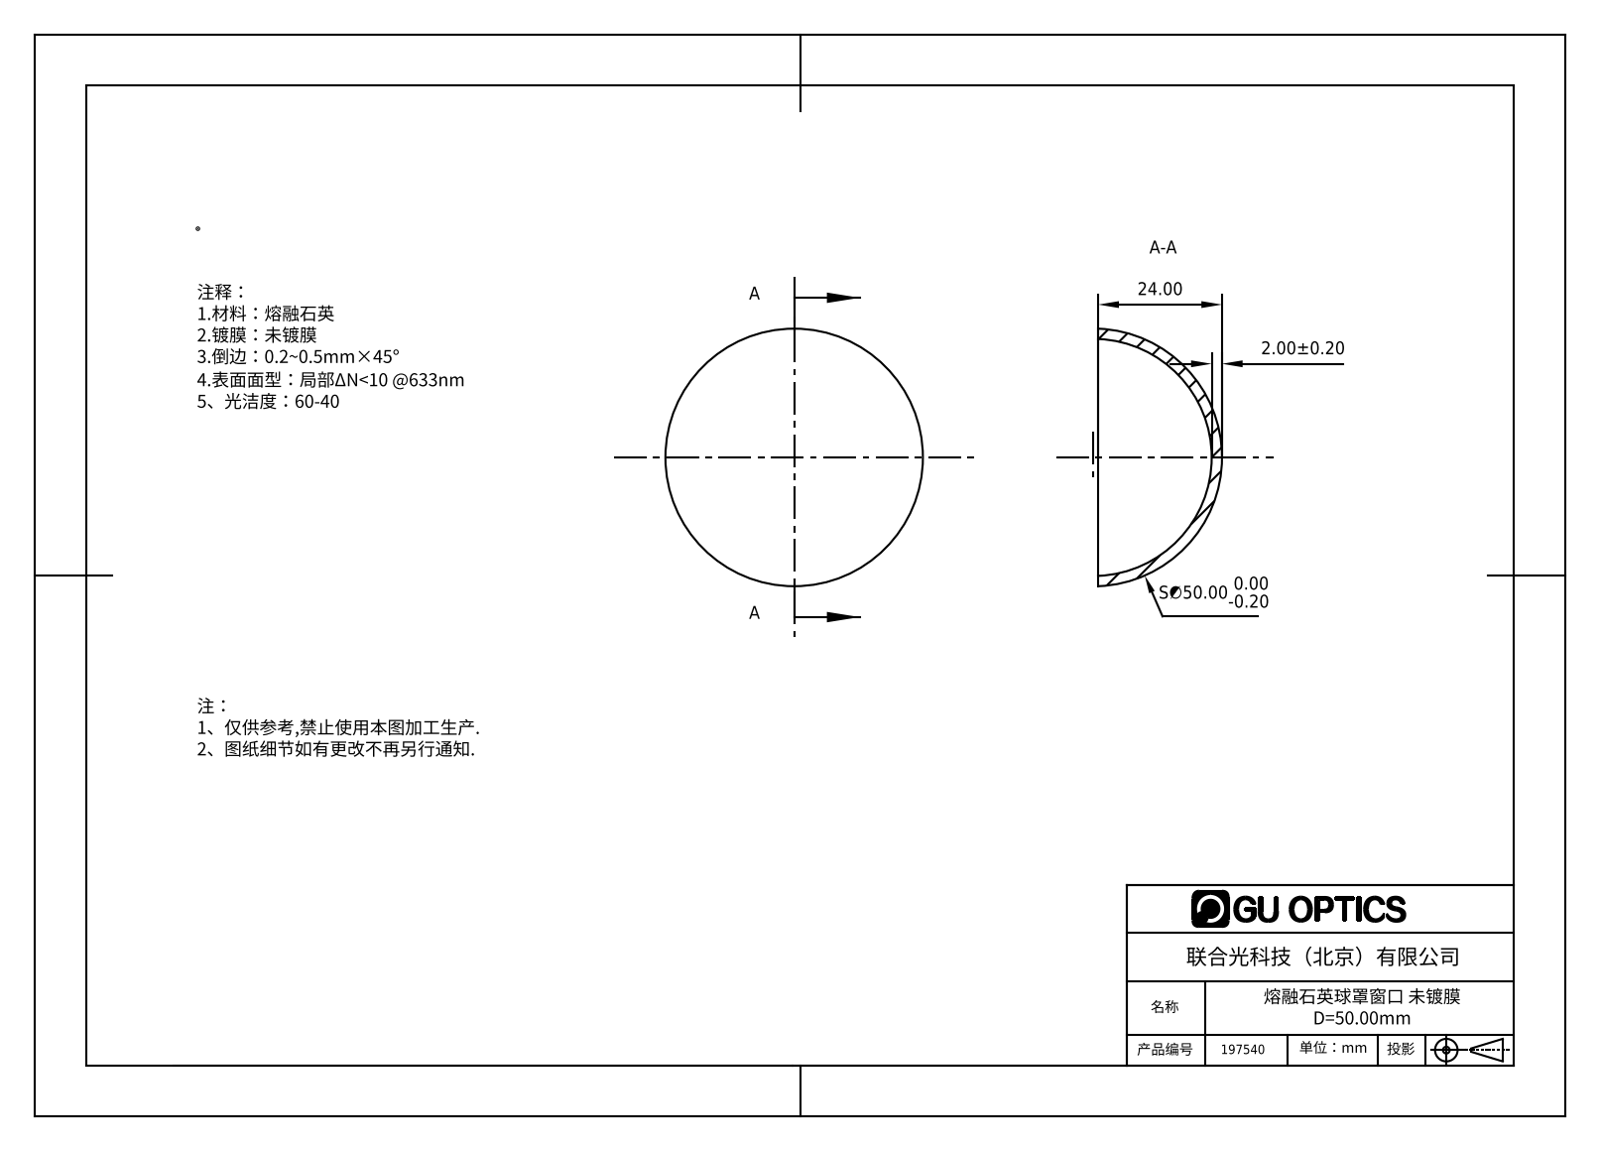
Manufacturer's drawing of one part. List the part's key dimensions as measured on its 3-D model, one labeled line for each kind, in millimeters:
Part name (STEP PRODUCT): 197536
STEP written by: SolidWorks 2016 (AUTOMOTIVE_DESIGN)
Units: millimetres
Bodies: 1 solid, 5 faces (1 planar, 0 cylindrical, 4 other)
Overall size (bounding box): 49.96 × 49.96 × 24
Volume: 6 938 mm³ · Surface area: 7 248 mm²
